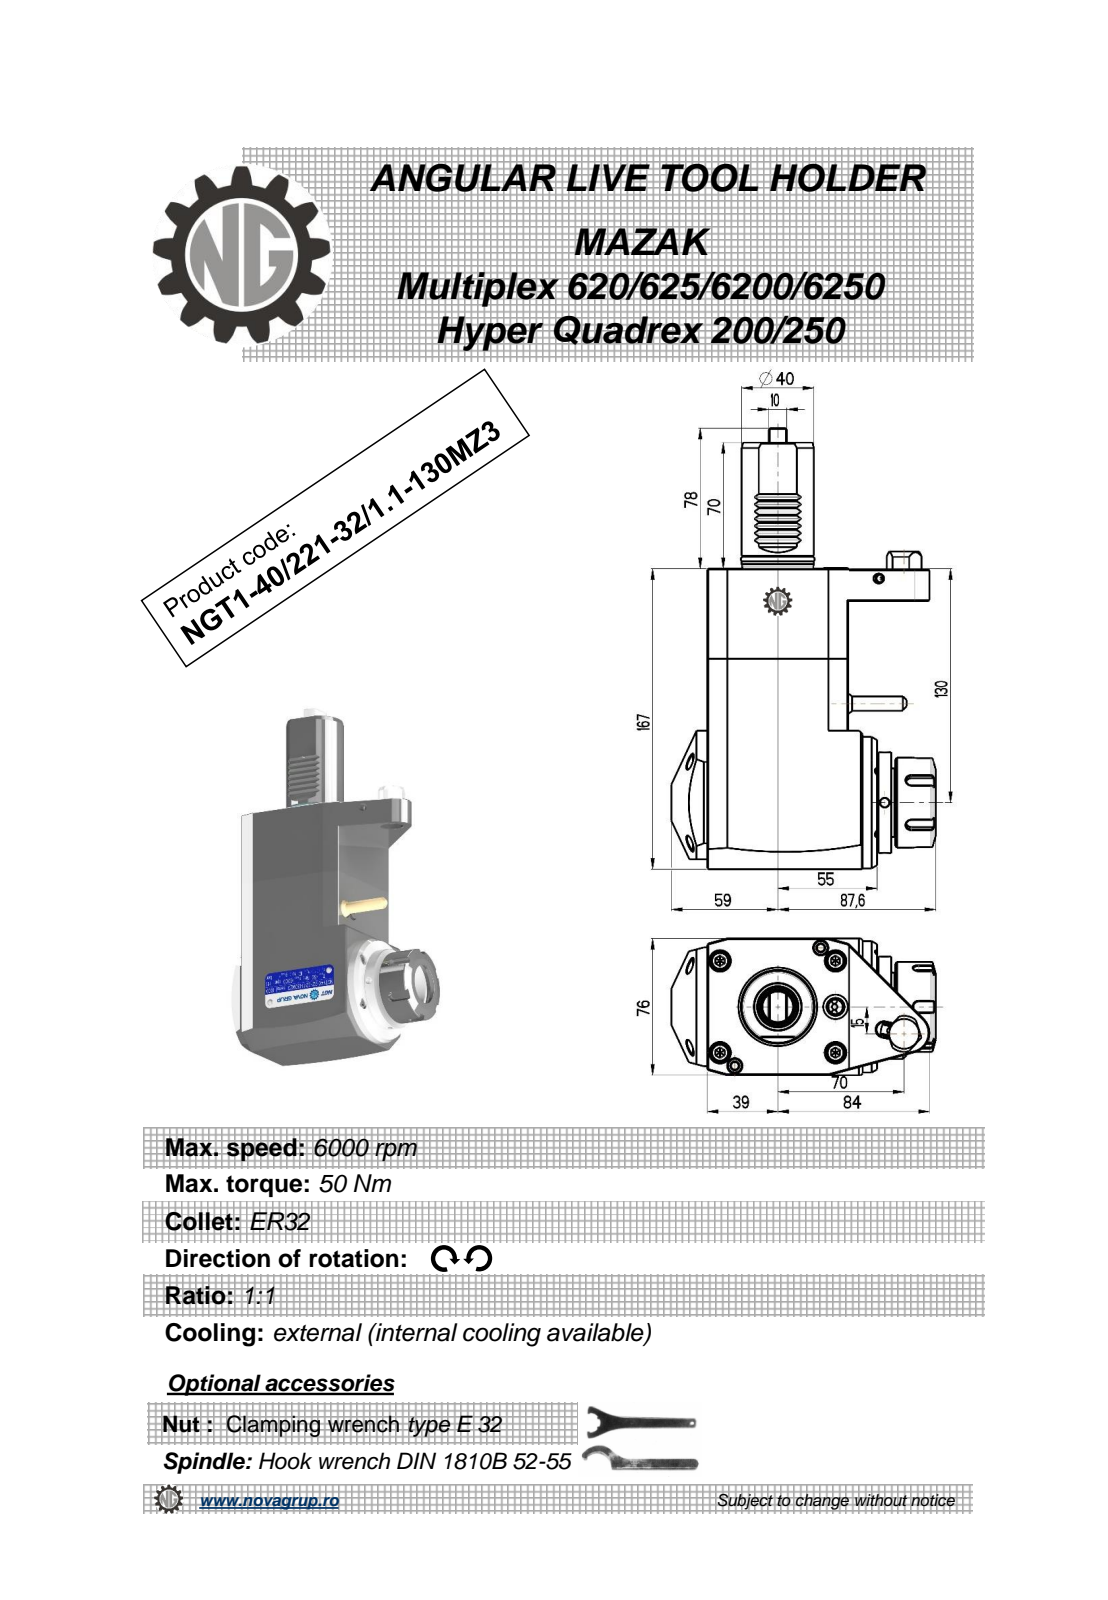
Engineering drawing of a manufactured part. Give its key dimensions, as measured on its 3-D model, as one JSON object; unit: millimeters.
{"part_name": "NGT1_40_221_32_1_1_130MZ3", "step_written_by": "PRO/ENGINEER BY PARAMETRIC TECHNOLOGY CORPORATION, 2010280 (CONFIG_CONTROL_DESIGN)", "units": "millimeters", "bodies": {"solids": 1, "faces": 284, "planar": 135, "cylindrical": 68, "other": 81}, "overall_size": [245, 146.6, 76], "volume_mm3": 1292000, "surface_area_mm2": 90126, "round_holes": [[3, 1], [5, 1], [8, 1], [27, 1]], "round_bosses_or_shafts": [[73, 1], [56, 1], [50, 1], [43, 1], [40, 1], [39.4, 1], [36.2, 1], [10, 1]], "partial_cylinders_radius": [[0.3, 7], [0.2, 6], [3, 5], [0.8, 2], [2.5, 2], [300, 2], [9, 1], [10, 1]], "face_to_face_distances": [76, 78, 167, 87.92, 18, 149, 8, 86, 5, 11], "hole_center_spacings": [60.42]}
